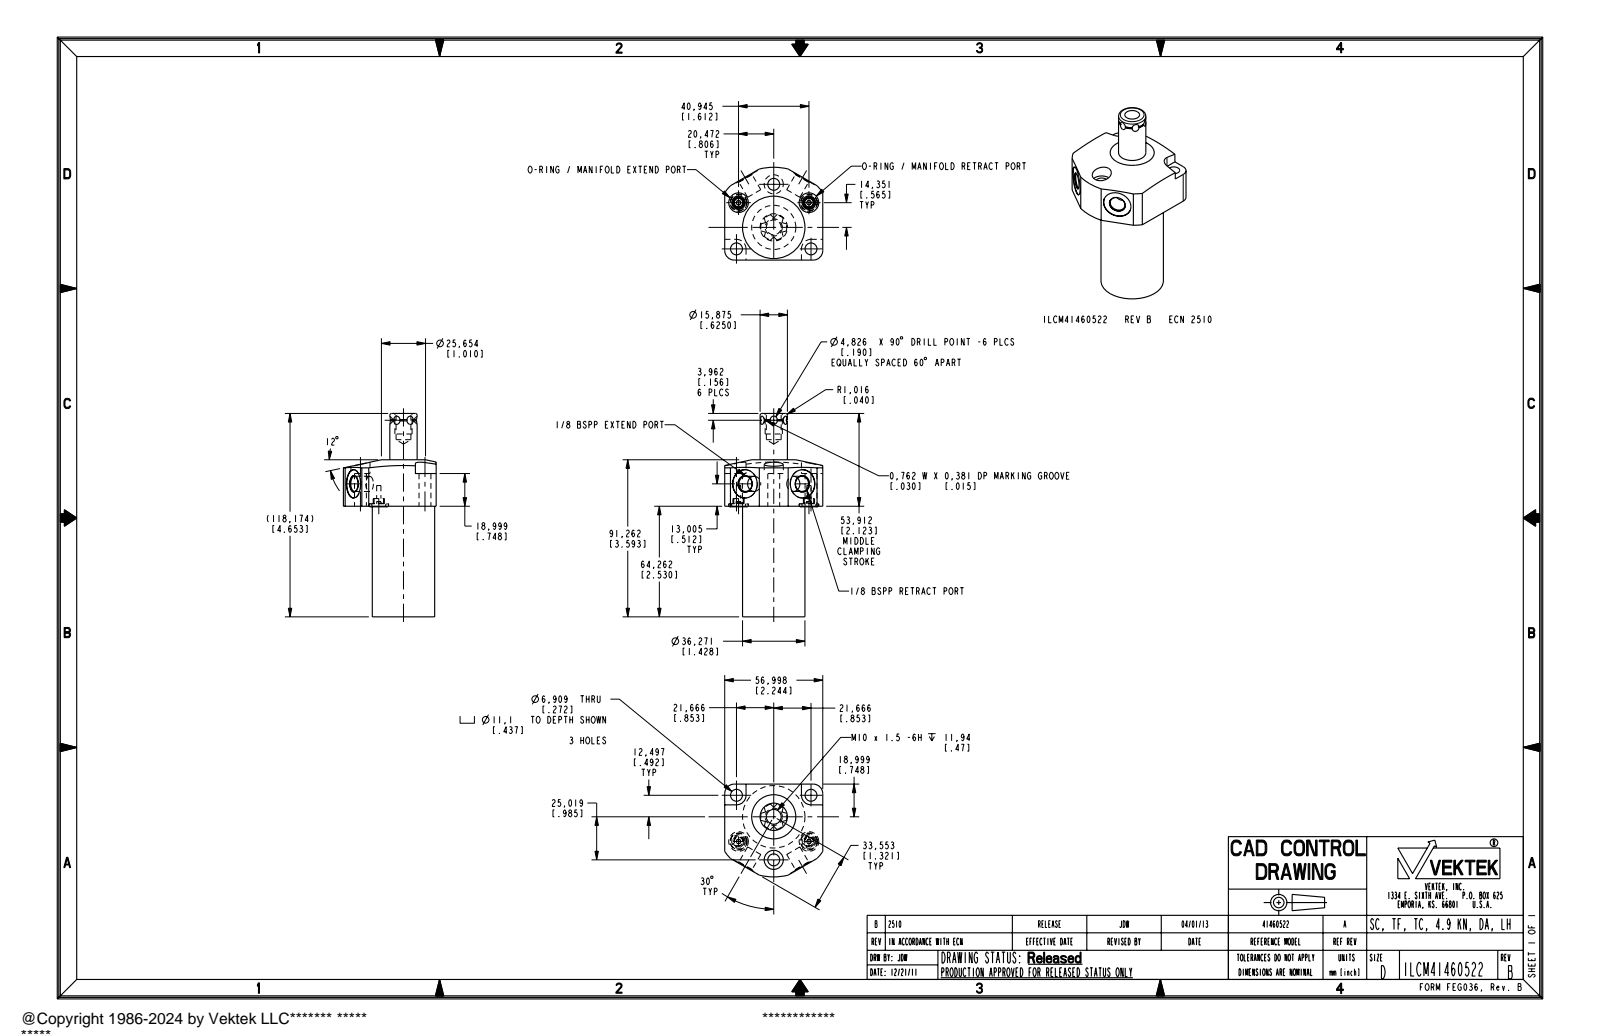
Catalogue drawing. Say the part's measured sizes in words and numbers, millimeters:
The part is named "ILCM41460522". Its 3-D file was written by "PRO/ENGINEER BY PARAMETRIC TECHNOLOGY CORPORATION, 2007460 (AUTOMOTIVE_DESIGN_CC2)". It is 1 solid with 148 faces: 59 planar, 55 cylindrical and 34 other. Overall it measures 118.17 by 57 by 53.92 millimeters. Its volume is 134 745 cubic millimeters and its surface area 22 354 square millimeters. Round holes: 3 of diameter 6.91, 2 of diameter 2.49, 2 of diameter 6.5, 2 of diameter 8.84, 2 of diameter 11.4, 2 of diameter 16.51, 1 of diameter 8.61, 1 of diameter 11.1. Round bosses or shafts: 2 of diameter 5.49, 1 of diameter 36.27, 1 of diameter 15.88, 1 of diameter 10.01. Partial cylindrical surfaces (rounded edges, fillets, slot ends): 2 of radius 5.55, 2 of radius 5.56, 1 of radius 7.56, 1 of radius 34.92. The main face-to-face distances are 64.26, 57, 91.26, 27, 83.26, 19, 8, 65.71, 1.45, 17.55. The hole center spacings are 25.02, 23.08, 25, 26.88, 43.33, 49.97, 40.94, 43.34.
